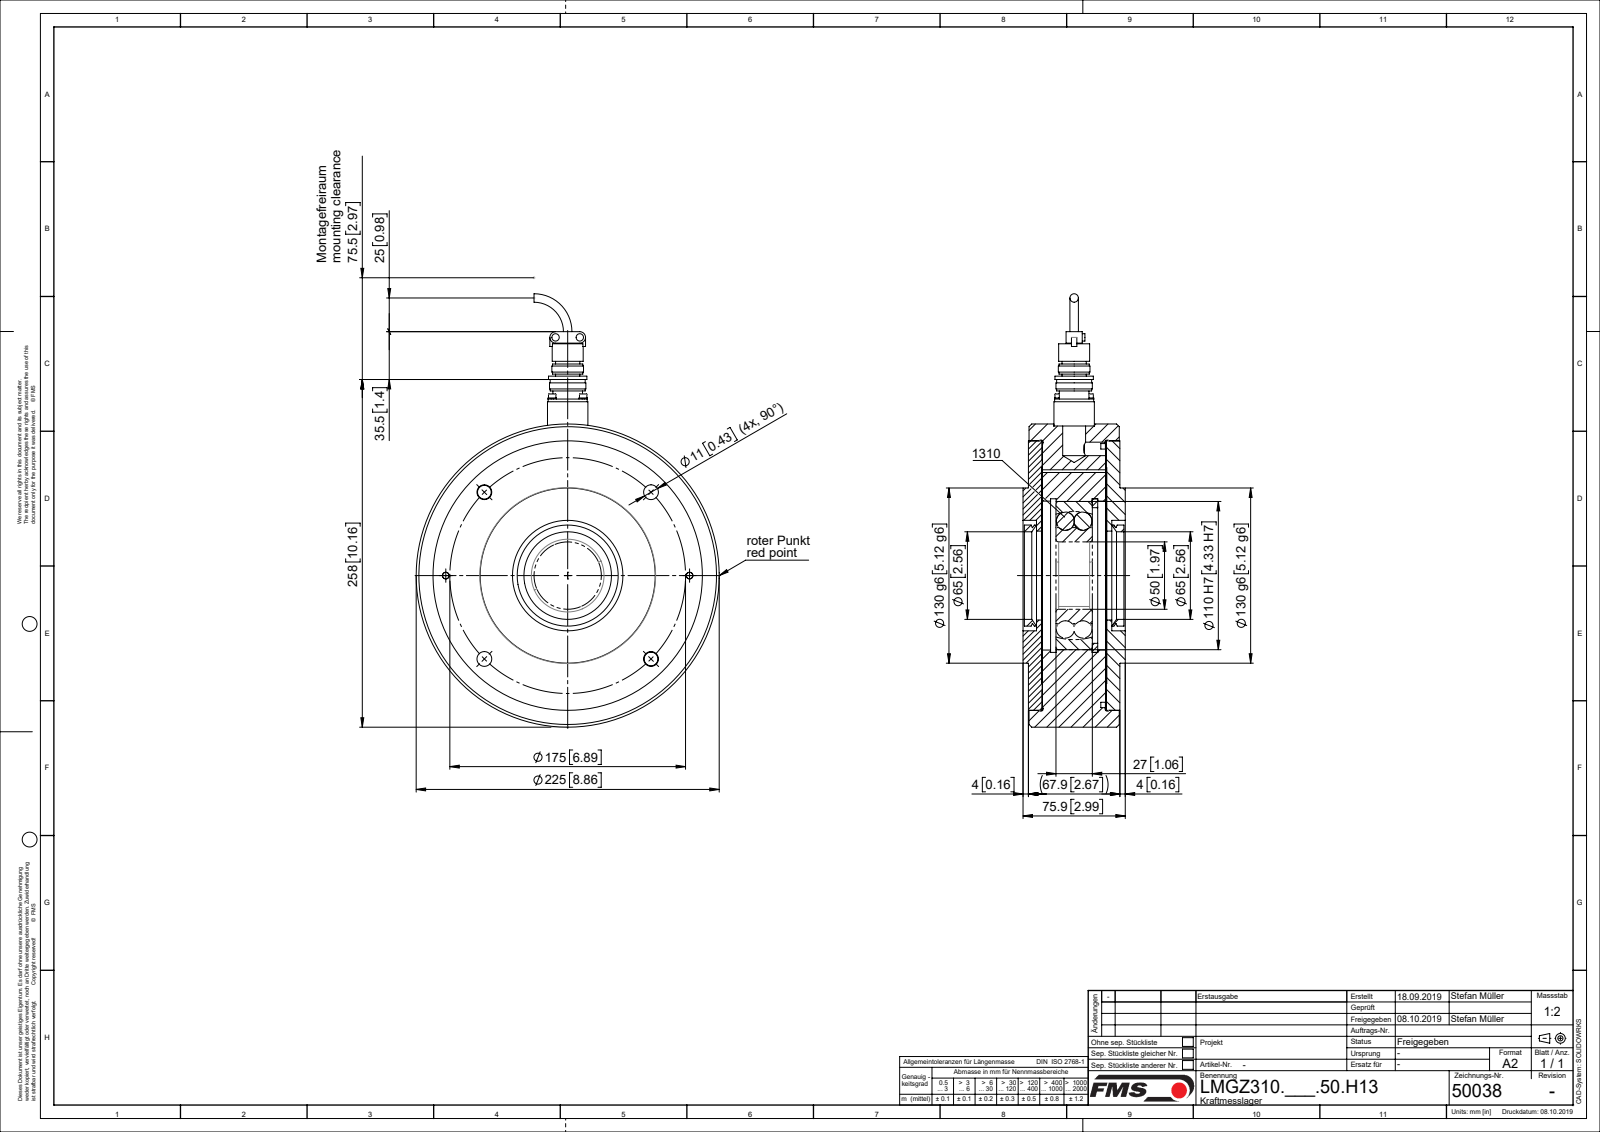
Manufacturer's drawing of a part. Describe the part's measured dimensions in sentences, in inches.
The part is named "ZEICHNUNG6; L50038; L4765504; TEIL1 (+8 more)". Its 3-D file was written by "Mechanical Desktop 2007 (CONFIG_CONTROL_DESIGN)". It is 21 solids with 418 faces: 114 planar, 240 cylindrical and 64 other. Overall it measures 12.663 by 8.858 by 2.988 inches. Its volume is 147.3 cubic inches and its surface area 607 square inches. Round holes: 6 of diameter 0.433, 4 of diameter 0.102, 4 of diameter 0.126, 4 of diameter 0.134, 4 of diameter 0.354, 2 of diameter 0.197, 2 of diameter 0.26, 1 of diameter 0.906, 1 of diameter 1.969, 1 of diameter 2.52, 1 of diameter 2.598, 1 of diameter 3.228. Round bosses or shafts: 6 of diameter 0.217, 4 of diameter 0.244, 4 of diameter 0.118, 4 of diameter 0.098, 2 of diameter 0.394, 2 of diameter 0.236, 1 of diameter 8.858, 1 of diameter 7.835. Partial cylindrical surfaces (rounded edges, fillets, slot ends): 2 of radius 0.167, 1 of radius 3.189, 1 of radius 3.386. The main face-to-face distances are 0.382, 1.86, 0.411, 0.423, 1.868, 0.402, 2.262, 2.272, 1.85, 0.394. The hole center spacings are 0.64, 0.906, 2.684, 3.445, 4.872, 6.474, 1.281, 3.563.
